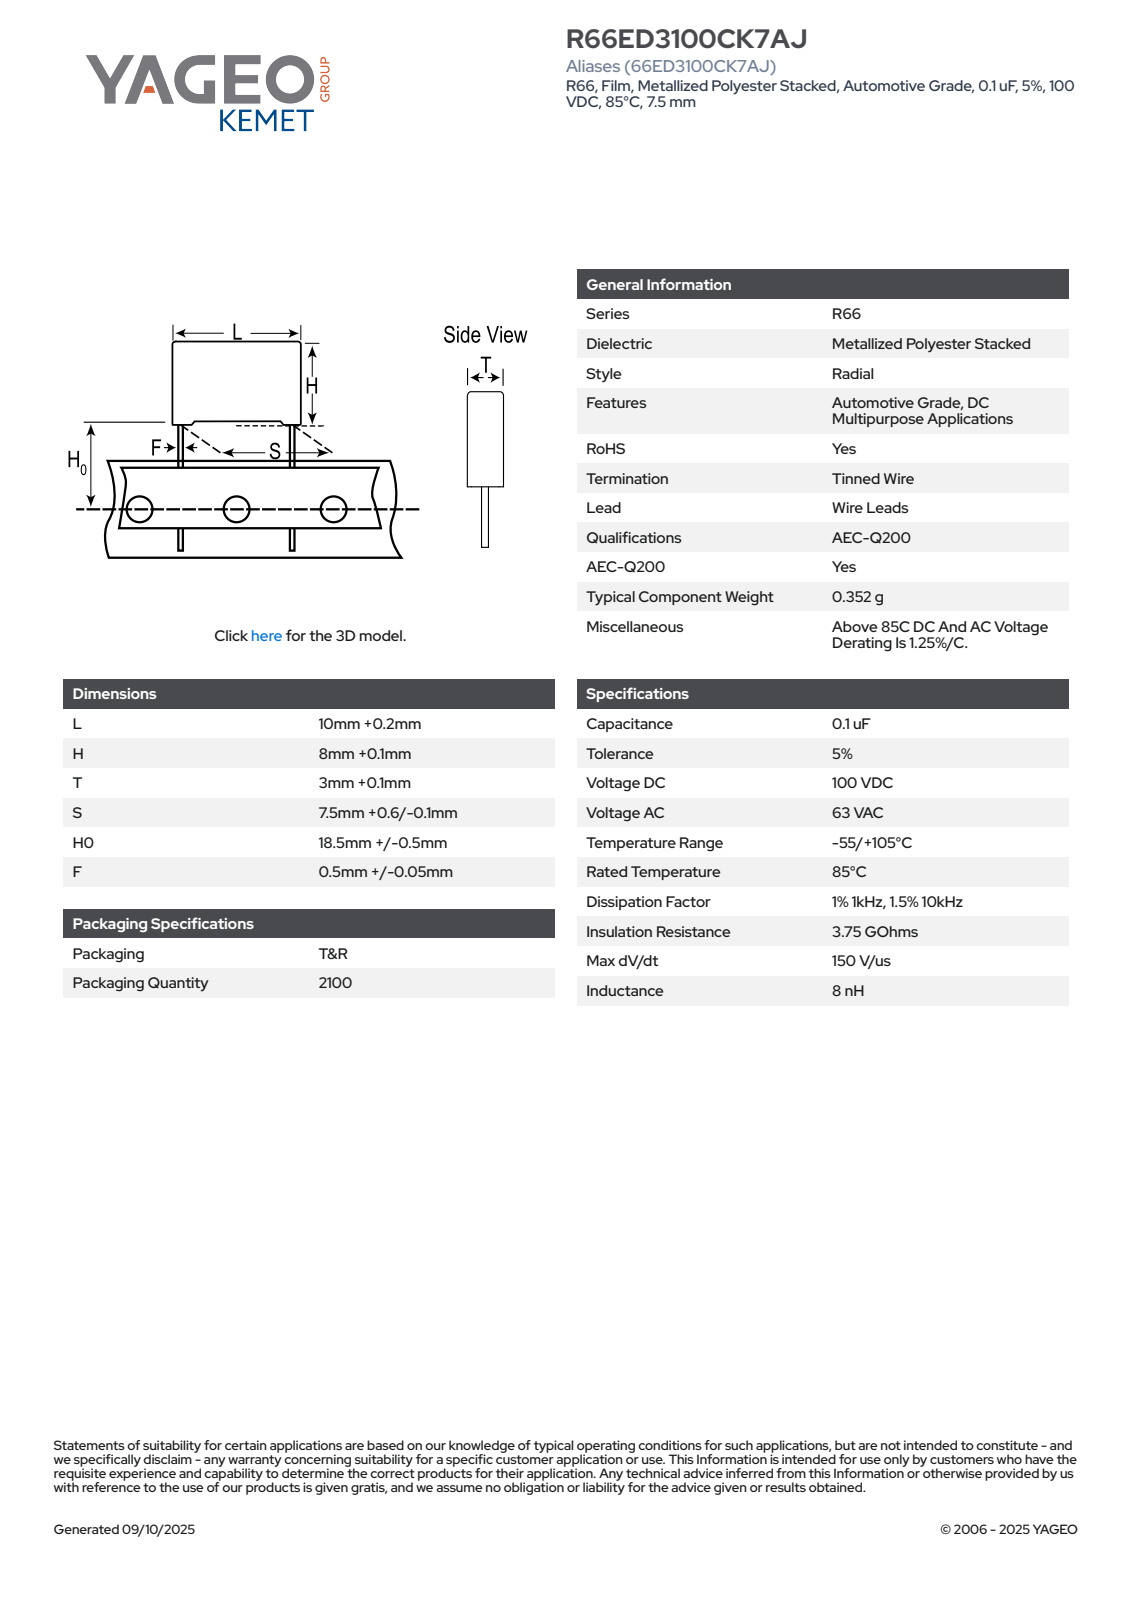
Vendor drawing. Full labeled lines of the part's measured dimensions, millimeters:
Part name (STEP PRODUCT): CFR_RB2_10X8X3_L10.2H8.1T3.1S7.5H019F0.55
STEP written by: SolidWorks 2020 (AUTOMOTIVE_DESIGN)
Units: millimetres
Bodies: 4 solids, 85 faces (77 planar, 8 cylindrical, 0 other)
Overall size (bounding box): 27.1 × 10.2 × 3.1
Volume: 246 mm³ · Surface area: 362 mm²
Round bosses / shafts (diameter × count): ⌀0.55 ×2
Partial cylindrical surfaces — rounded edges, fillets, slot ends (radius × count): R0.5 ×4
Main face-to-face distances: 3.1, 10.2, 7.35, 0.34, 2.76, 2.42, 0.75, 8.1, 9.86, 0.47
